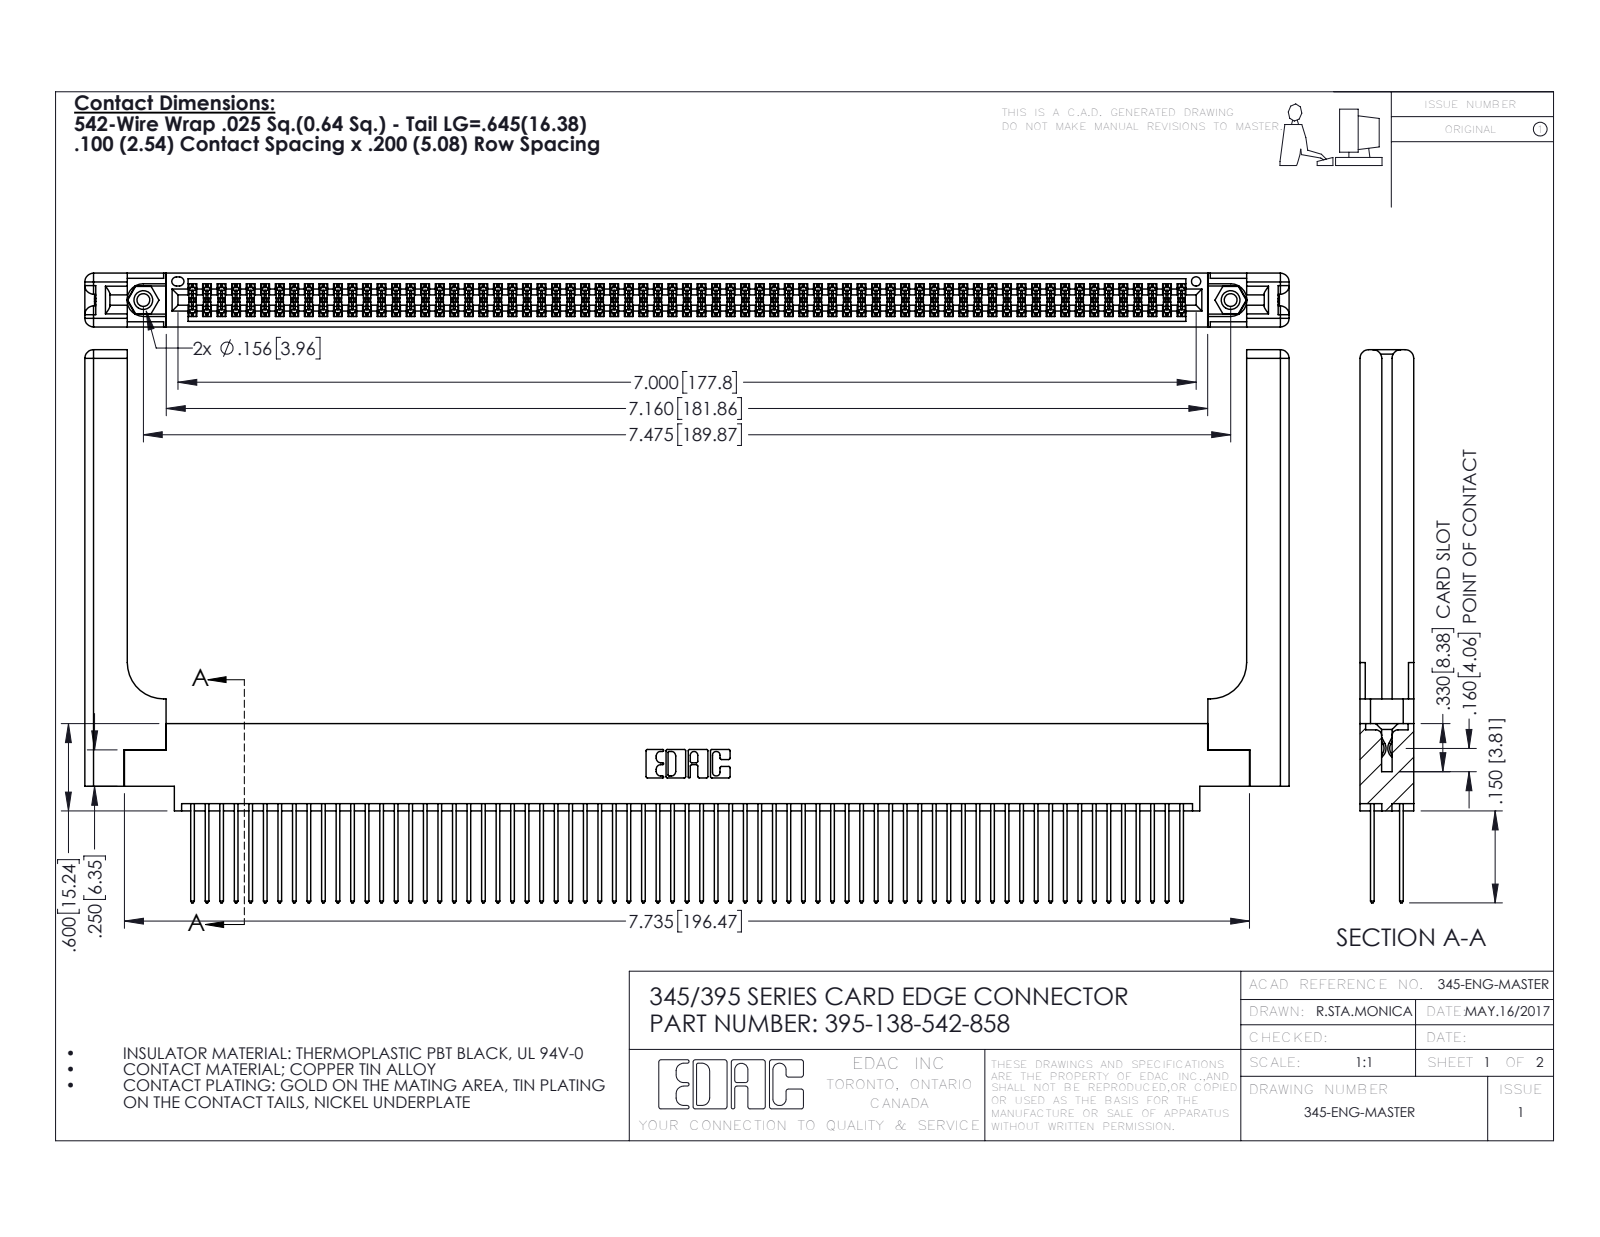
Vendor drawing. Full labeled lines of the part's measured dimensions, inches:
Part name (STEP PRODUCT): 345-220-058_345-220-058; 345-250-001_345-250-001-102; 395-138-542-858; 345 Part_0.170 Offset - 0.156 Dia-TH (+1 more)
STEP written by: SolidWorks 2016 (CONFIG_CONTROL_DESIGN)
Units: inches
Bodies: 143 solids, 7286 faces (4786 planar, 2440 cylindrical, 60 other)
Overall size (bounding box): 8.279 × 3.802 × 0.37
Volume: 1.811 in³ · Surface area: 62.12 in²
Round holes (diameter × count): ⌀0.089 ×2, ⌀0.125 ×2, ⌀0.156 ×2, ⌀0.064 ×1
Round bosses / shafts (diameter × count): ⌀0.155 ×2
Partial cylindrical surfaces — rounded edges, fillets, slot ends (radius × count): R0.006 ×207, R0.01 ×138, R0.01 ×22, R0.06 ×16, R0.007 ×6, R0.031 ×6, R0.026 ×3, R0.014 ×2
Main face-to-face distances: 0.072, 0.298, 0.37, 0.098, 0.272, 0.025, 0.2, 0.225, 0.175, 0.148
Hole centre spacings: 0.27, 7.239, 7.475
